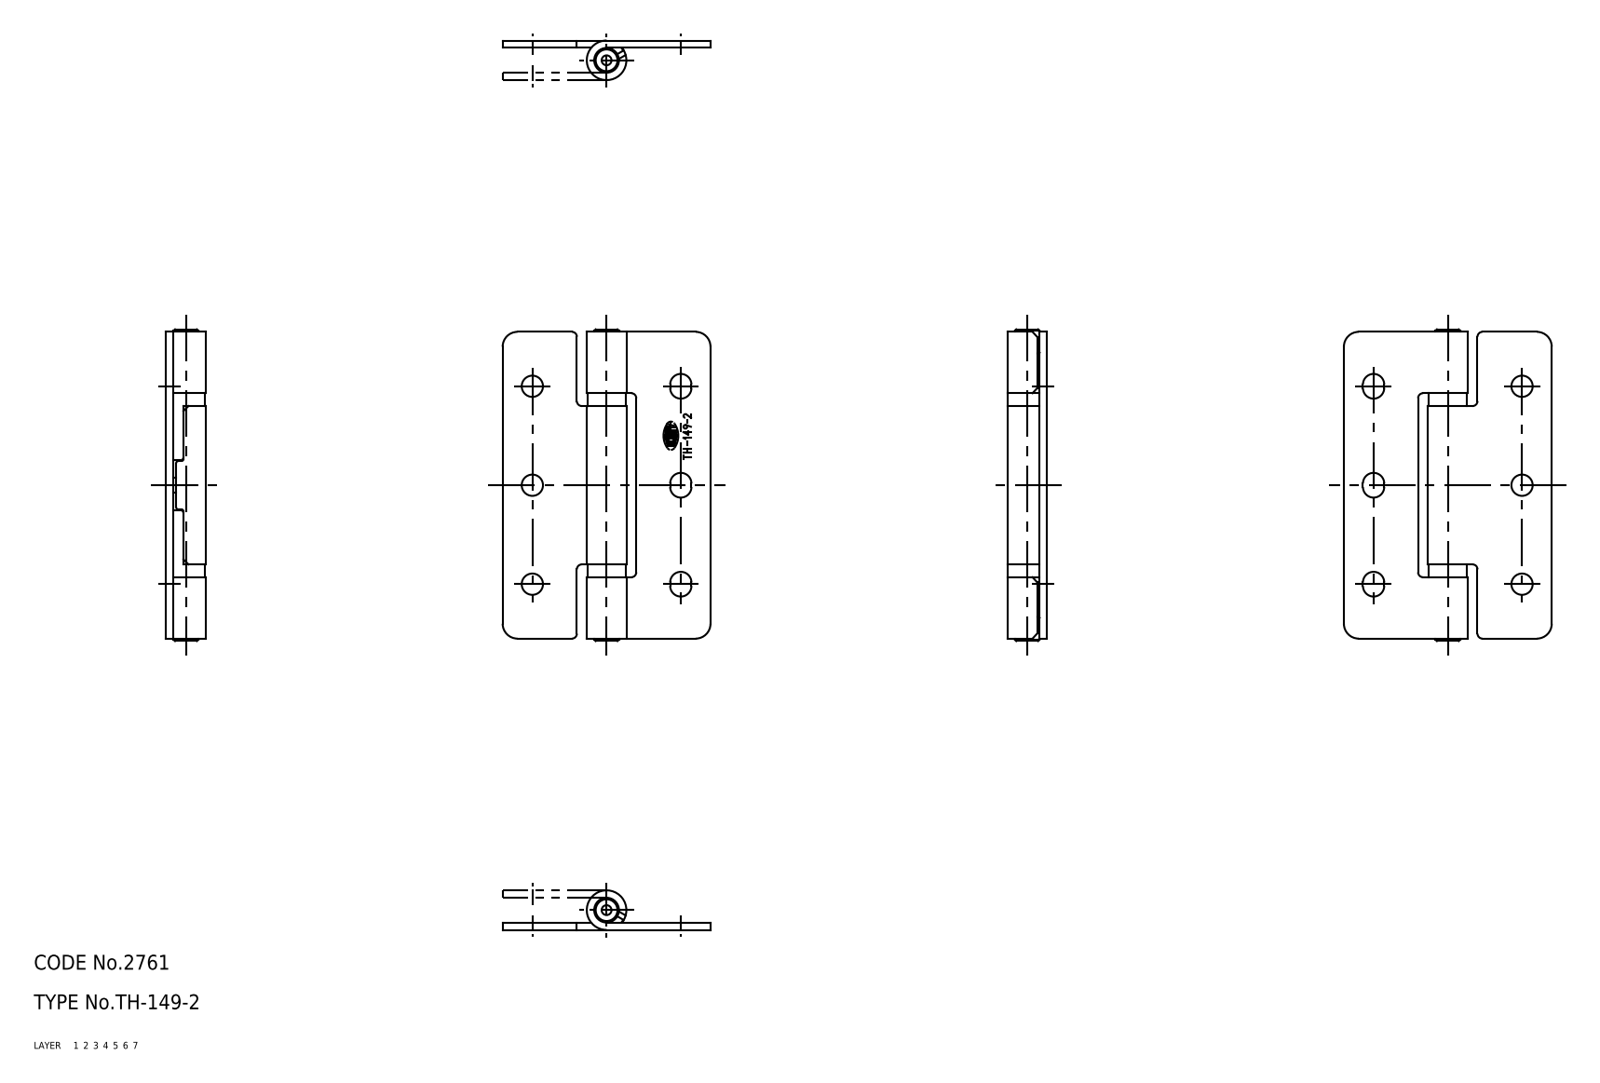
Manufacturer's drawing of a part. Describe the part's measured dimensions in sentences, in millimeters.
The part is named "67115812; 67115825; 67115838; 67115851 (+2 more)". Its 3-D file was written by "CADfix (AUTOMOTIVE_DESIGN)". It is 6 solids with 118 faces: 0 planar, 0 cylindrical and 118 other. Overall it measures 63 by 42 by 8 millimeters. Its volume is 5 833 cubic millimeters and its surface area 8 898 square millimeters.
